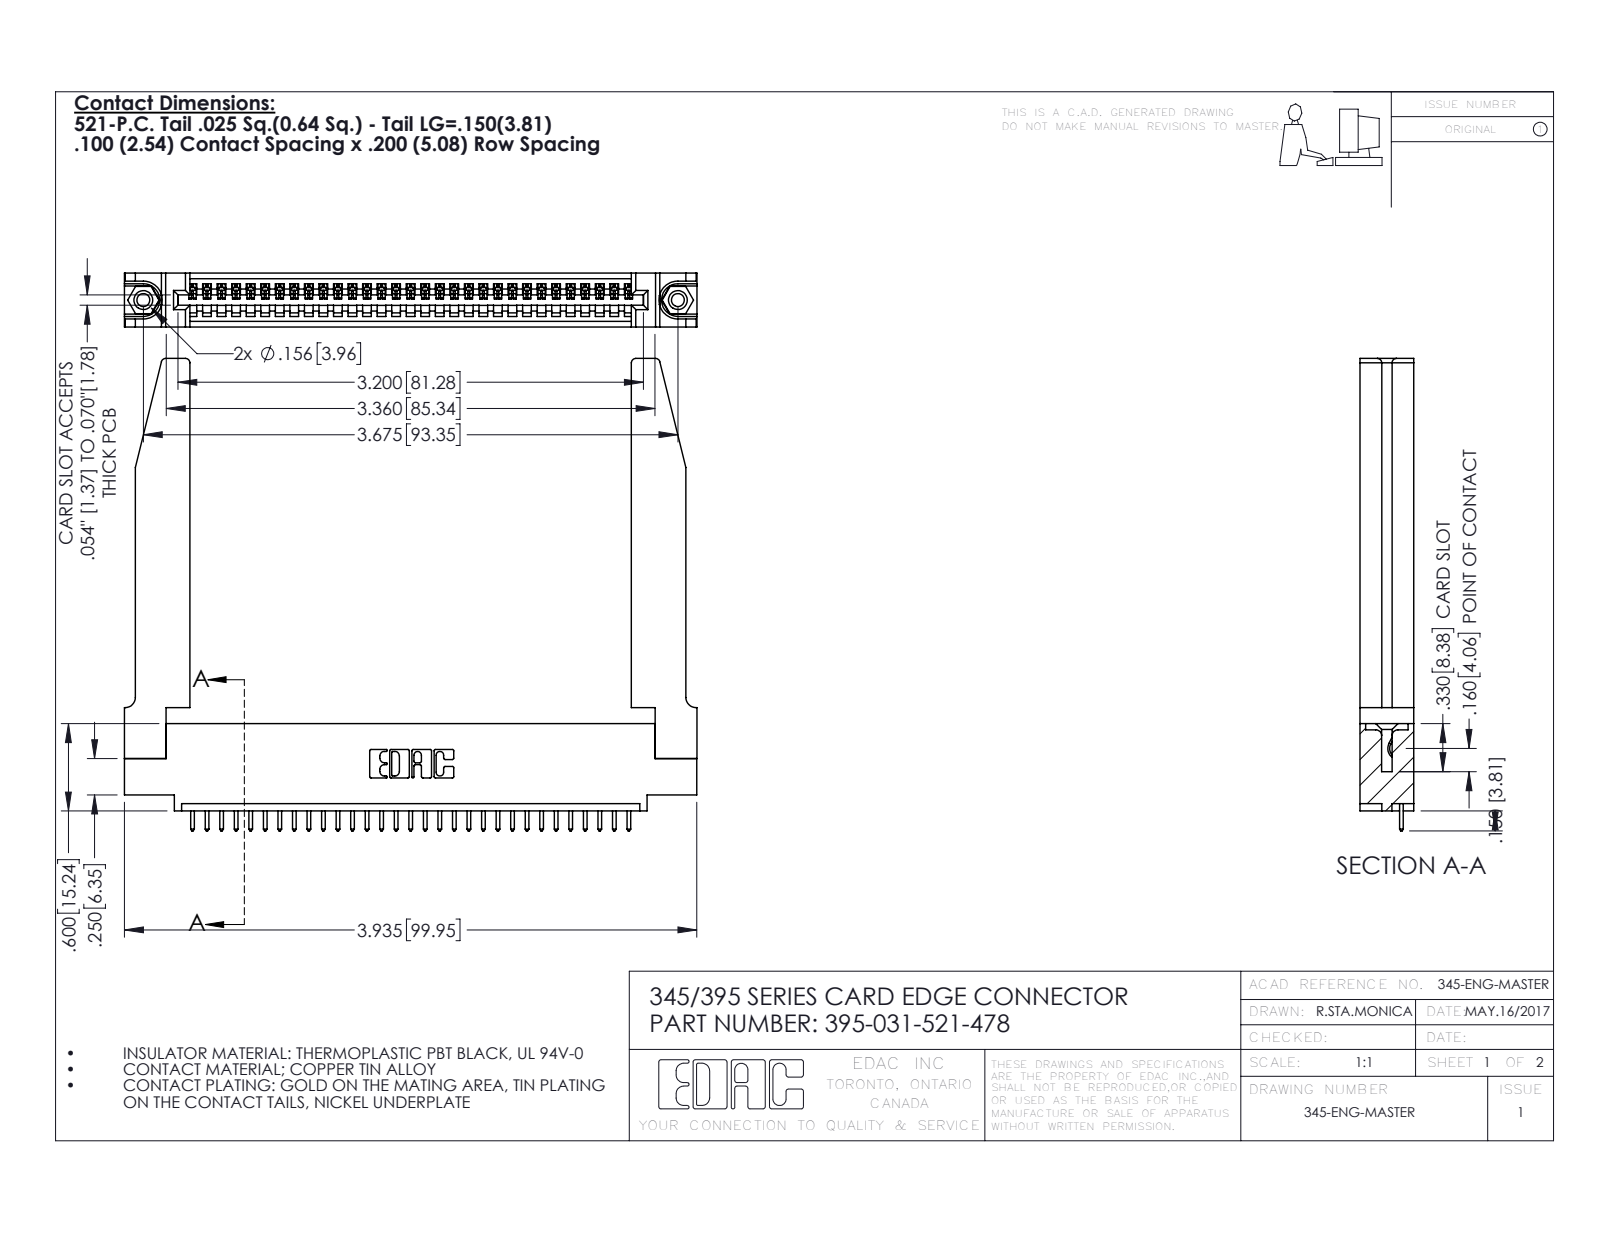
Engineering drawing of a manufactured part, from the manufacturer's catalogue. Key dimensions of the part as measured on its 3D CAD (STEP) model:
Part name (STEP PRODUCT): 345-250-001_345-250-001-102; 345-220-078_345-220-078; 345-292-001_345-293-121; 395-031-521-478 (+1 more)
STEP written by: SolidWorks 2016 (CONFIG_CONTROL_DESIGN)
Units: inches
Bodies: 36 solids, 2162 faces (1466 planar, 644 cylindrical, 52 other)
Overall size (bounding box): 3.936 × 3.247 × 0.37
Volume: 1.038 in³ · Surface area: 29.01 in²
Round holes (diameter × count): ⌀0.089 ×2, ⌀0.125 ×2, ⌀0.156 ×2, ⌀0.064 ×1
Round bosses / shafts (diameter × count): ⌀0.155 ×2
Partial cylindrical surfaces — rounded edges, fillets, slot ends (radius × count): R0.006 ×62, R0.01 ×62, R0.01 ×22, R0.03 ×8, R0.007 ×6, R0.031 ×6, R0.026 ×3, R0.031 ×2
Main face-to-face distances: 0.37, 0.072, 0.298, 0.2, 0.098, 0.272, 0.025, 0.15, 0.148, 0.225
Hole centre spacings: 0.27, 3.44, 3.675
